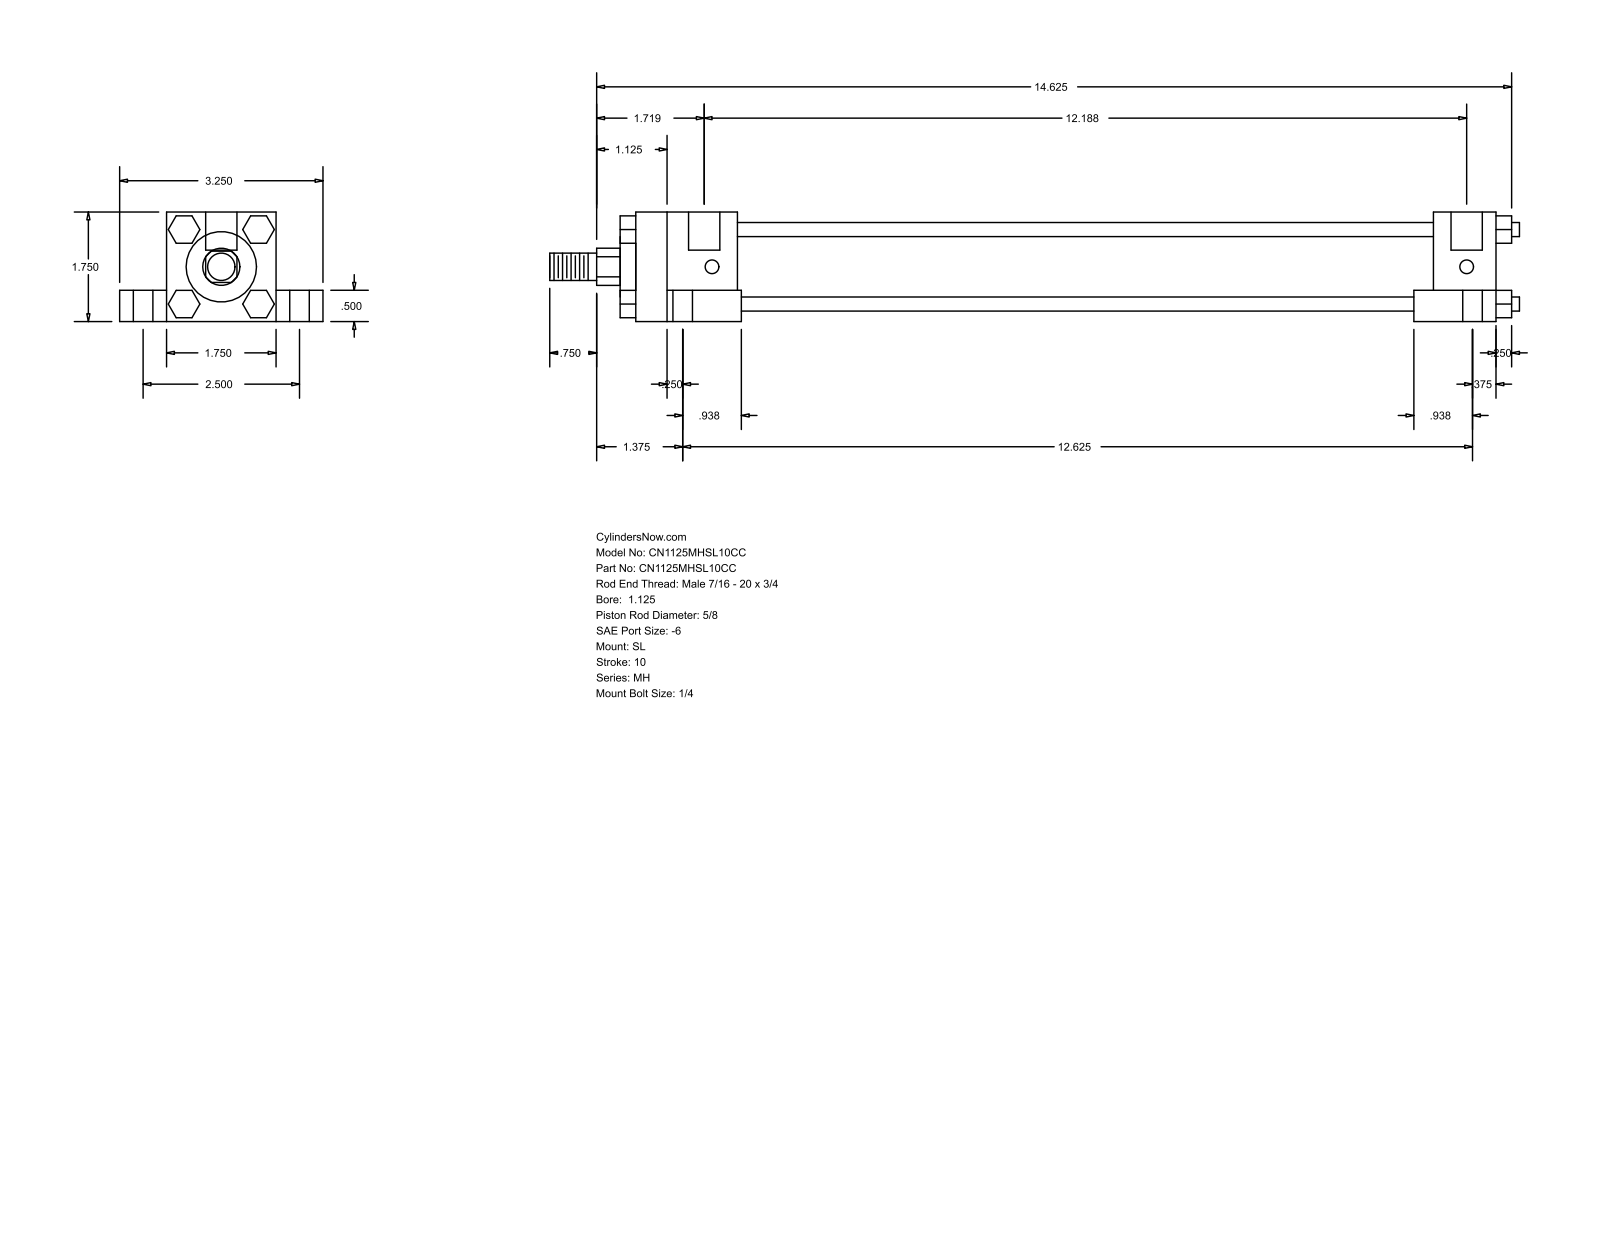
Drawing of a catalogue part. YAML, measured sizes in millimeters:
part_name: "MH_SL__0112_0.625"
step_written_by: "GSSL Pune (CONFIG_CONTROL_DESIGN)"
units: millimeters
bodies: {solids: 0, faces: 150, planar: 114, cylindrical: 36, other: 0}
overall_size: [393.7, 82.55, 44.45]
round_holes:
  - {diameter: 5.56, count: 4}
  - {diameter: 7.94, count: 4}
  - {diameter: 14.29, count: 4}
  - {diameter: 12.7, count: 2}
round_bosses_or_shafts:
  - {diameter: 5.71, count: 4}
  - {diameter: 34.92, count: 1}
  - {diameter: 28.57, count: 1}
  - {diameter: 15.88, count: 1}
  - {diameter: 11.11, count: 1}
partial_cylinders:
  - {radius: 7.54, count: 1}
face_to_face_distances: [44.46, 19.04, 12.7, 31.76, 63.5, 11.11, 47.62, 282.58, 307.97, 25.39]
hole_center_spacings: [31.84, 32.23, 32.93, 63.5, 306.39, 310.4, 313.55, 316.72]
